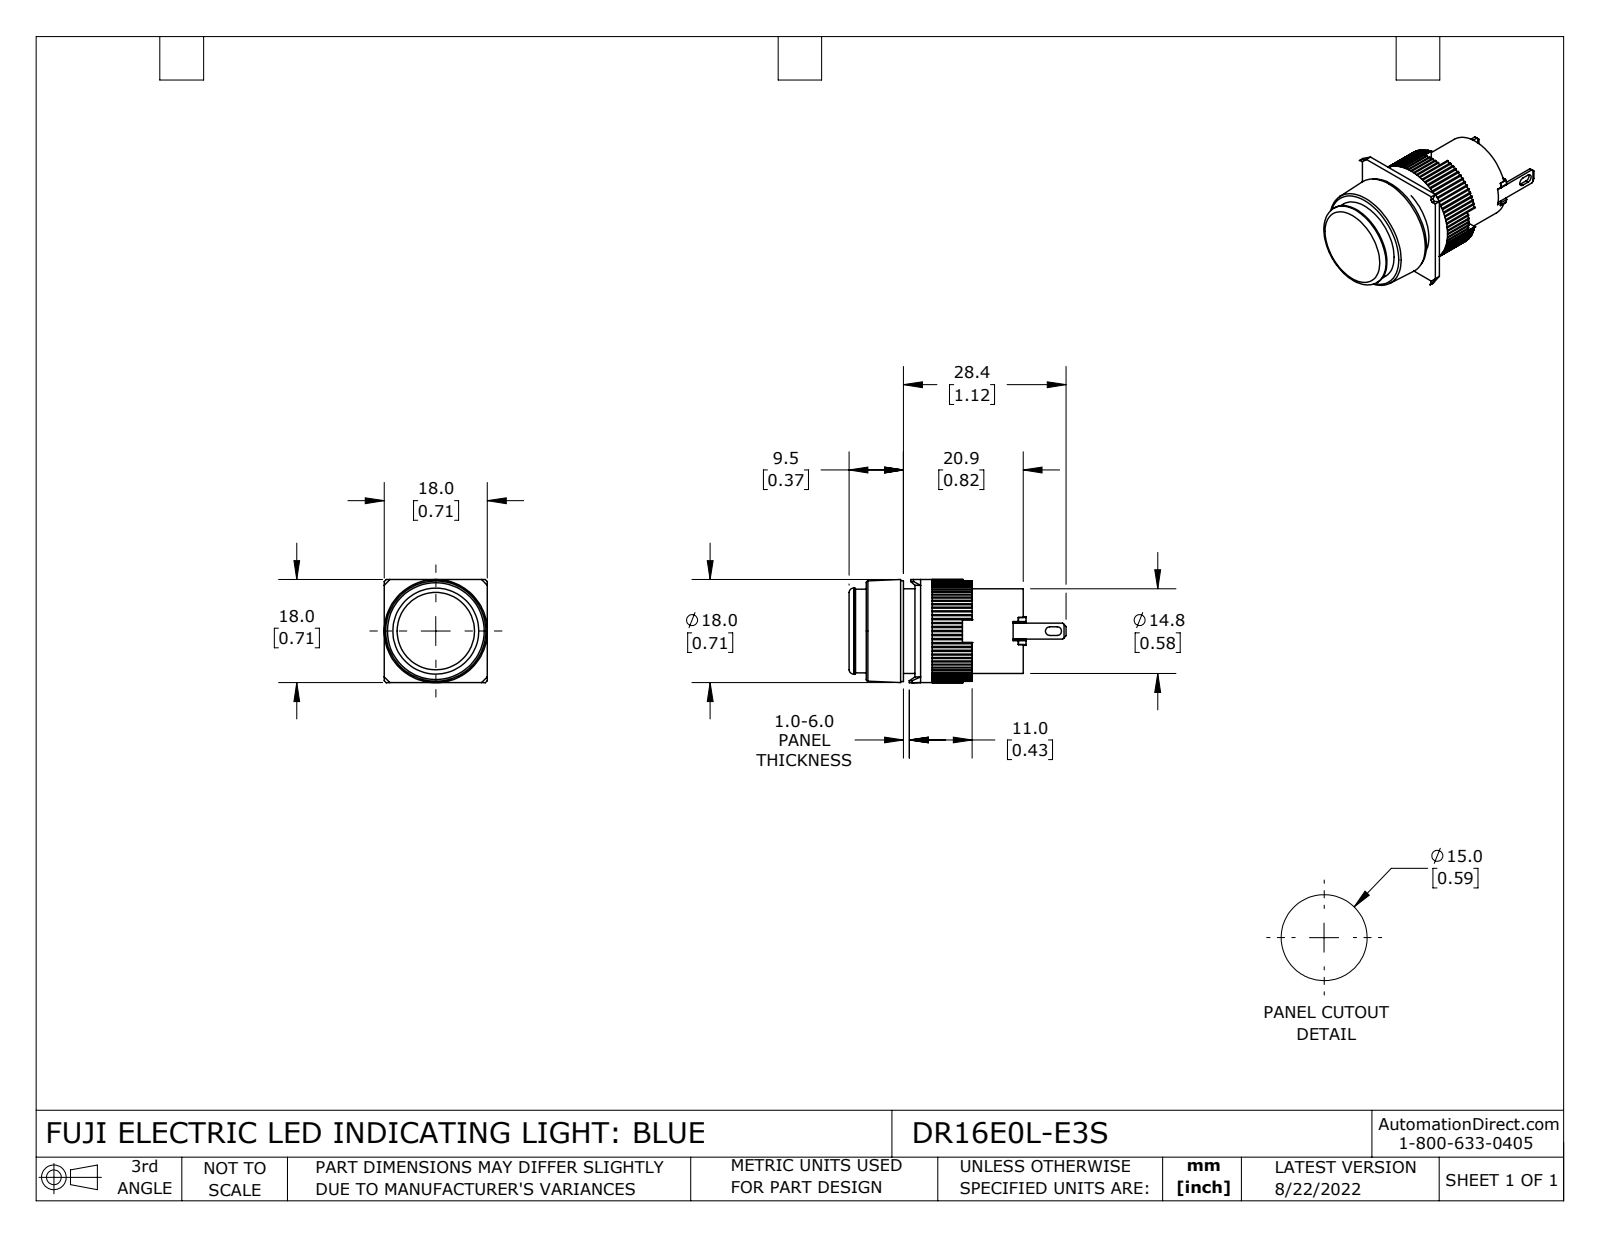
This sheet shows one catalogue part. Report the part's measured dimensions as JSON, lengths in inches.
{"part_name": "DR16E0L-E3S", "step_written_by": "SolidWorks 2021 (CONFIG_CONTROL_DESIGN)", "units": "inches", "bodies": {"solids": 10, "faces": 476, "planar": 295, "cylindrical": 171, "other": 10}, "overall_size": [1.492, 0.709, 0.709], "volume_in3": 0.349, "surface_area_in2": 7.224, "round_holes": [[0.543, 1], [0.575, 1], [0.583, 1]], "round_bosses_or_shafts": [[0.709, 1], [0.693, 1], [0.591, 1]], "partial_cylinders_radius": [[0.01, 80], [0.008, 8], [0.03, 2]], "face_to_face_distances": [0.138, 0.35, 0.705, 0.354, 0.492, 0.213, 0.453, 0.843, 0.098, 0.039]}
